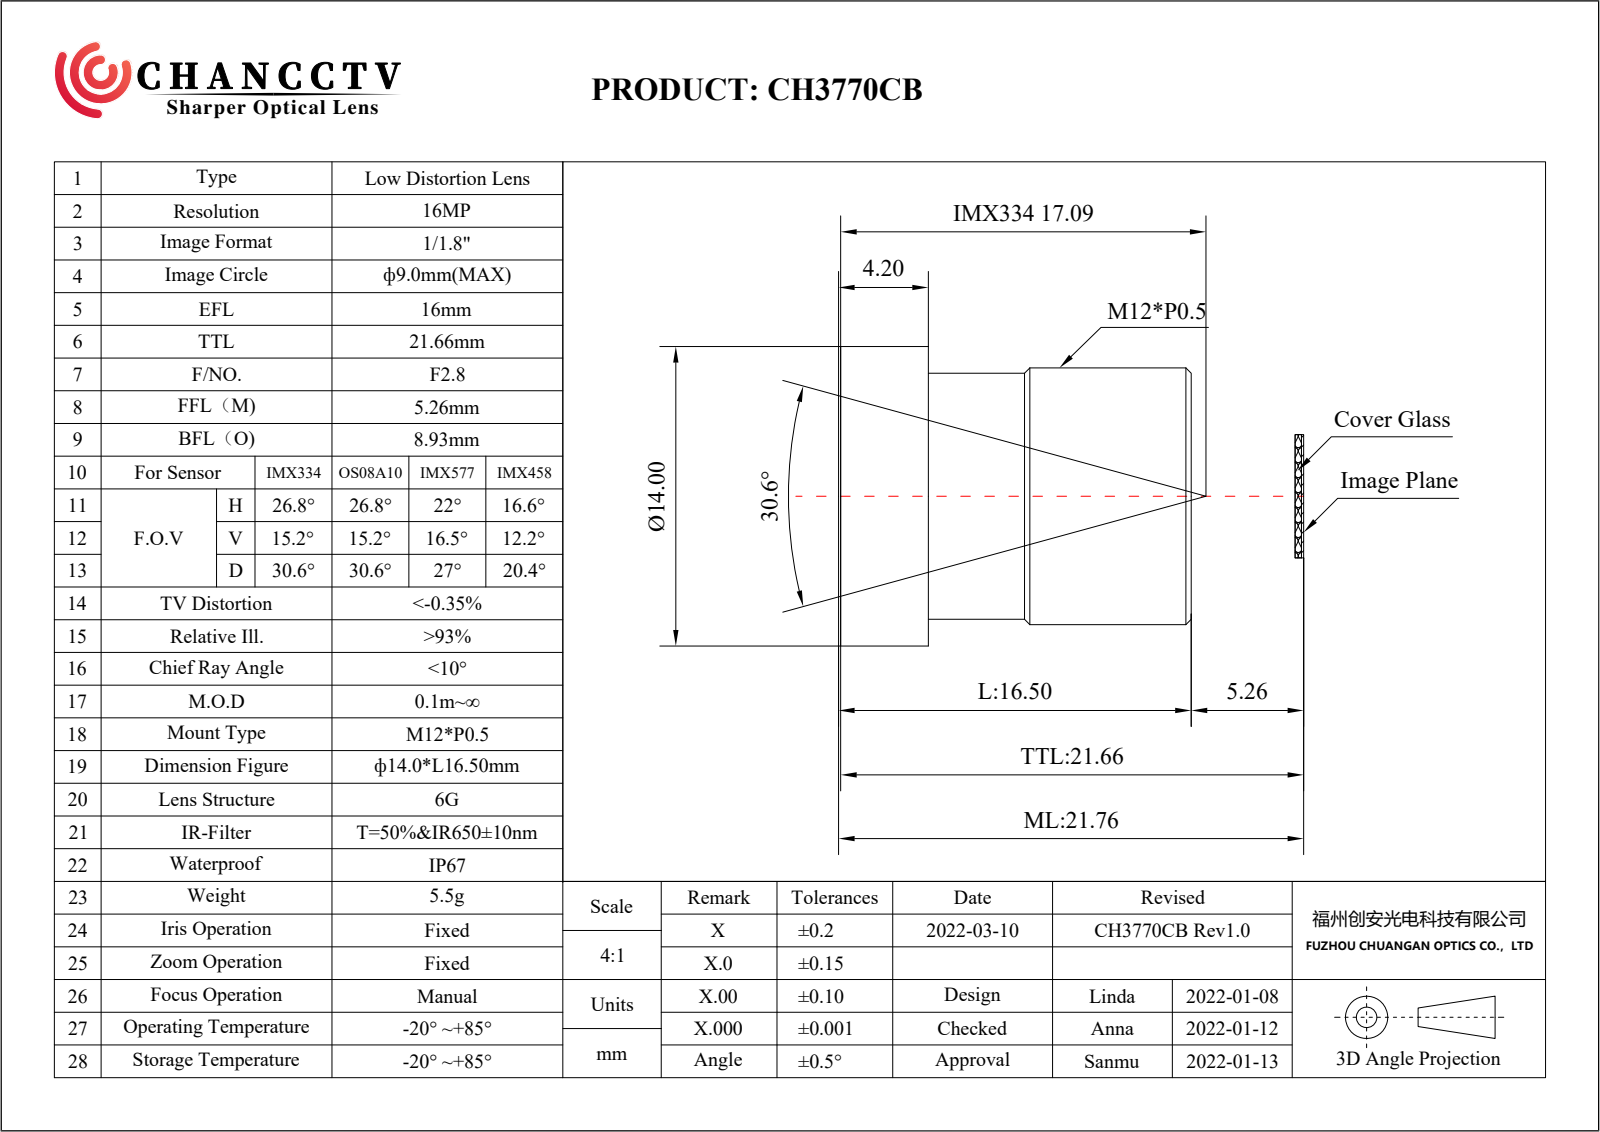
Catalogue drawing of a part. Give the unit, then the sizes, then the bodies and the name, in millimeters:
Units: millimetres
Overall size (bounding box): 16.32 × 14 × 14
Round holes (diameter × count): ⌀10 ×1
Round bosses / shafts (diameter × count): ⌀14 ×1, ⌀12 ×1, ⌀11.2 ×1
Main face-to-face distances: 11.82, 4.2, 16.02, 16.32, 12.12
Volume: 1 824 mm³ · Surface area: 1 187 mm²
Bodies: 1 solid, 59 faces (4 planar, 34 cylindrical, 21 other)
Part name (STEP PRODUCT): CH3770CB
STEP written by: CREO PARAMETRIC BY PTC INC, 2019010 (CONFIG_CONTROL_DESIGN)
